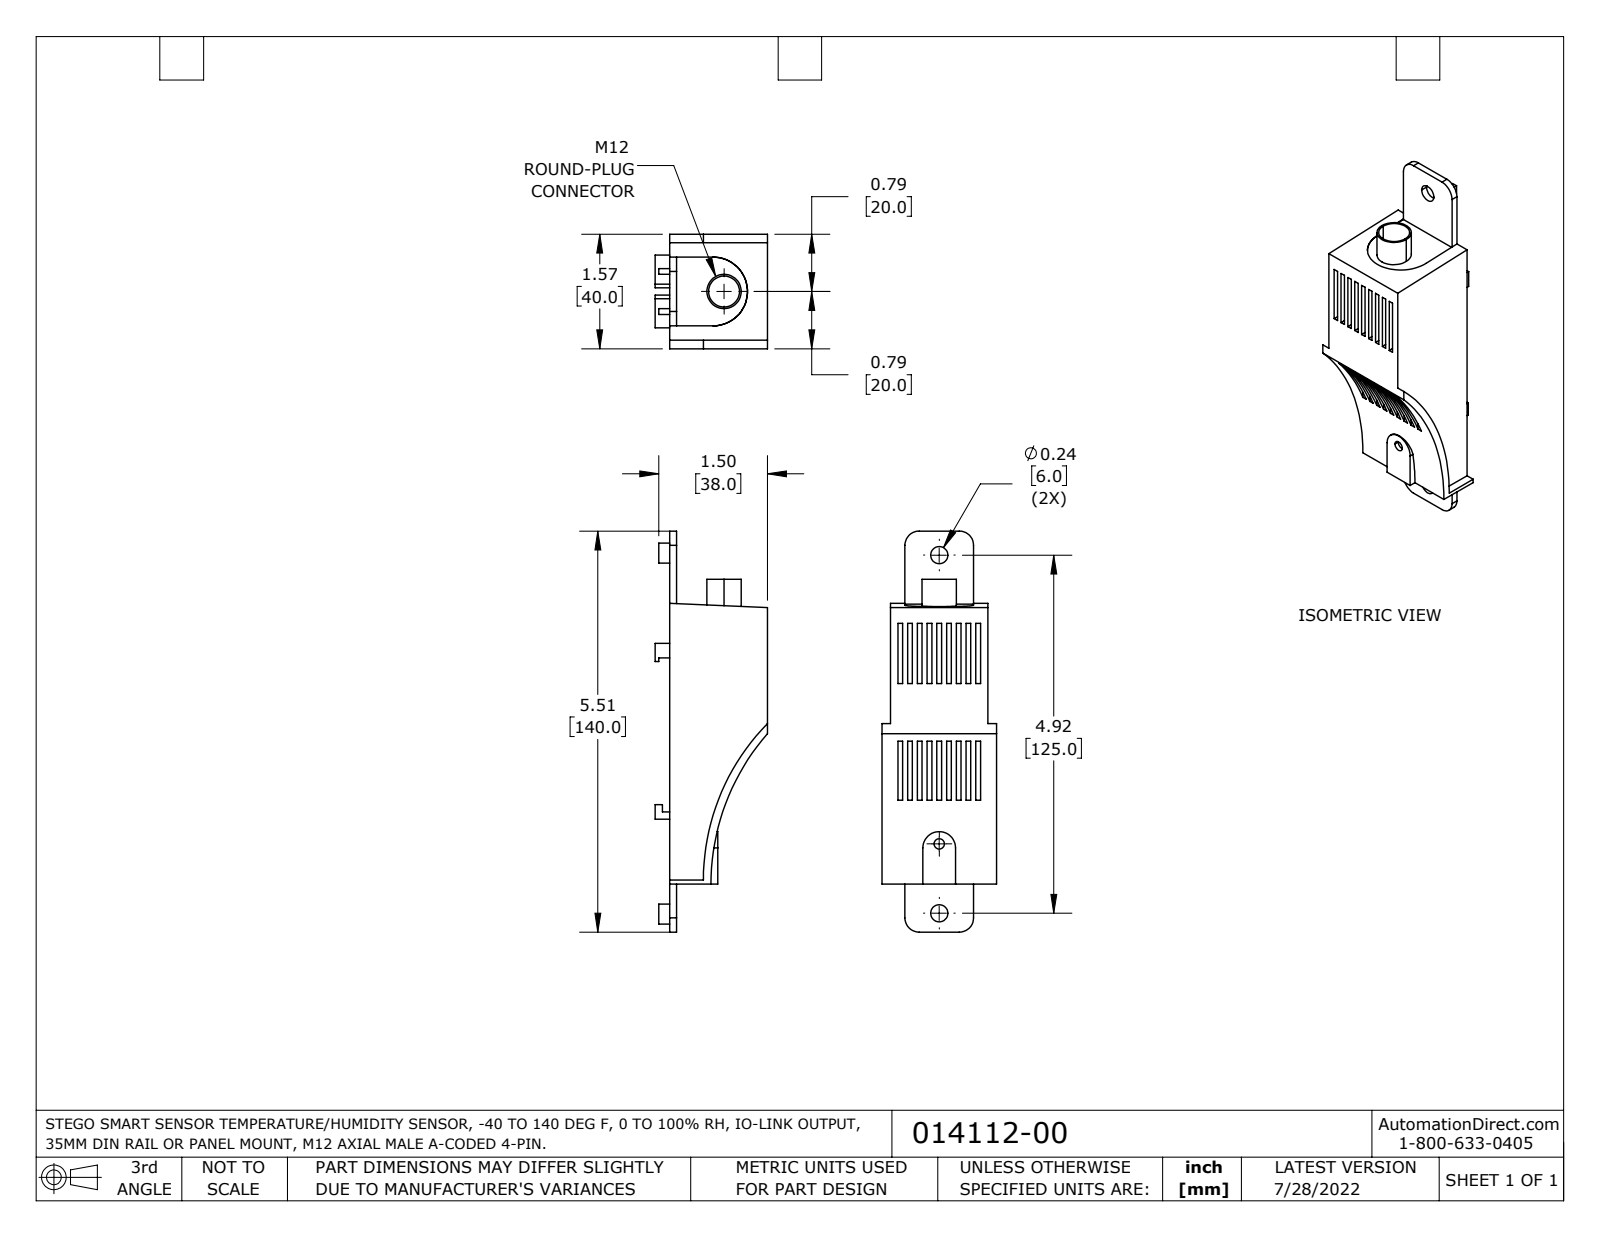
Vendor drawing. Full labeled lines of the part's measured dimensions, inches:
Part name (STEP PRODUCT): 014112-00
STEP written by: SolidWorks 2021 (AUTOMOTIVE_DESIGN)
Units: inches
Bodies: 1 solid, 188 faces (169 planar, 19 cylindrical, 0 other)
Overall size (bounding box): 5.512 × 1.575 × 1.546
Volume: 5.339 in³ · Surface area: 38.61 in²
Round holes (diameter × count): ⌀0.236 ×2, ⌀0.142 ×1, ⌀0.425 ×1
Round bosses / shafts (diameter × count): ⌀0.472 ×1
Partial cylindrical surfaces — rounded edges, fillets, slot ends (radius × count): R0.197 ×4, R0.224 ×1, R0.472 ×1, R3.059 ×1, R3.135 ×1
Main face-to-face distances: 0.134, 0.268, 0.402, 0.535, 0.065, 0.669, 0.199, 0.069, 1.339, 0.333
Hole centre spacings: 0.953, 3.969, 4.921
